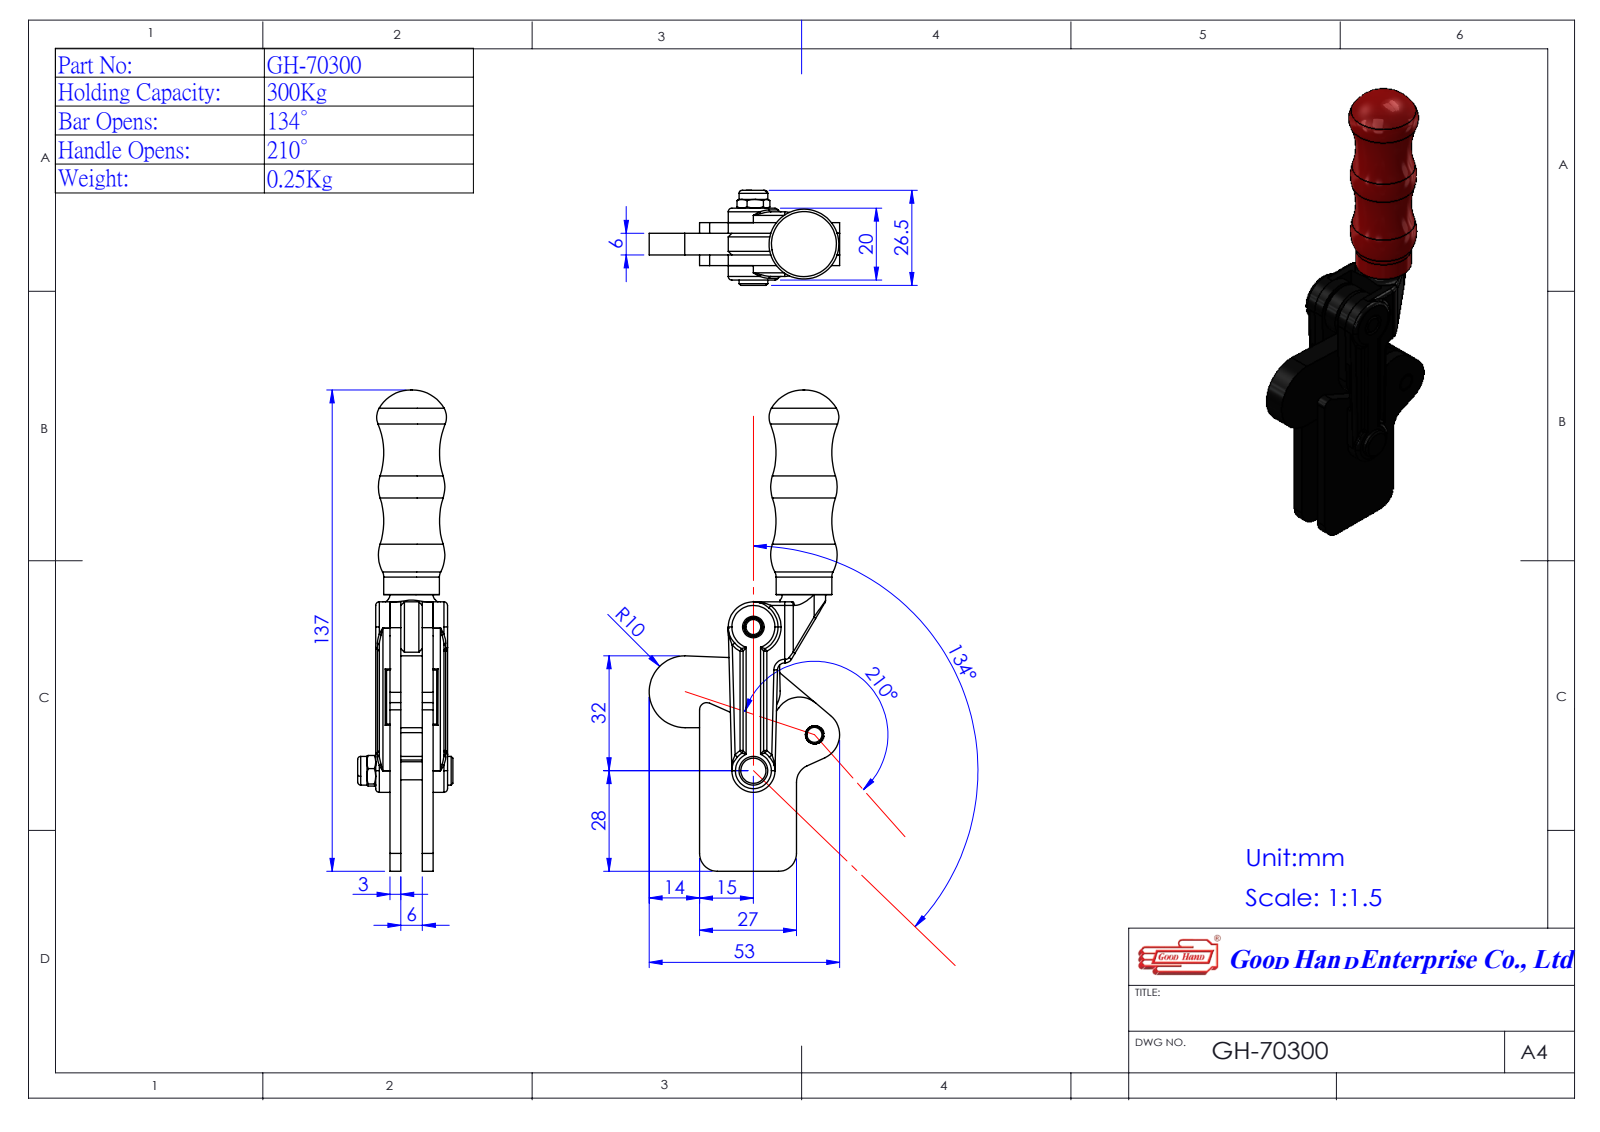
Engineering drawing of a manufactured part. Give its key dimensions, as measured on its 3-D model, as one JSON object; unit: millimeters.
{"part_name": "Group2^GH-70300(簡化); GH-70300(簡化); 37030008簡化); Group1^GH-70300(簡化) (+1 more)", "step_written_by": "SolidWorks 2016 (AUTOMOTIVE_DESIGN)", "units": "millimeters", "bodies": {"solids": 4, "faces": 214, "planar": 55, "cylindrical": 76, "other": 83}, "overall_size": [134.02, 53, 23.95], "volume_mm3": 37580, "surface_area_mm2": 19469, "round_holes": [[4, 4]], "round_bosses_or_shafts": [[14, 1]], "partial_cylinders_radius": [[1, 19], [5, 5], [2, 3], [7, 3], [10, 3], [6, 2], [8, 1]], "face_to_face_distances": [3, 9, 6, 12, 4, 13, 7, 16, 20, 27], "hole_center_spacings": [18, 19.72, 20.43, 22.02, 34.55, 40]}
